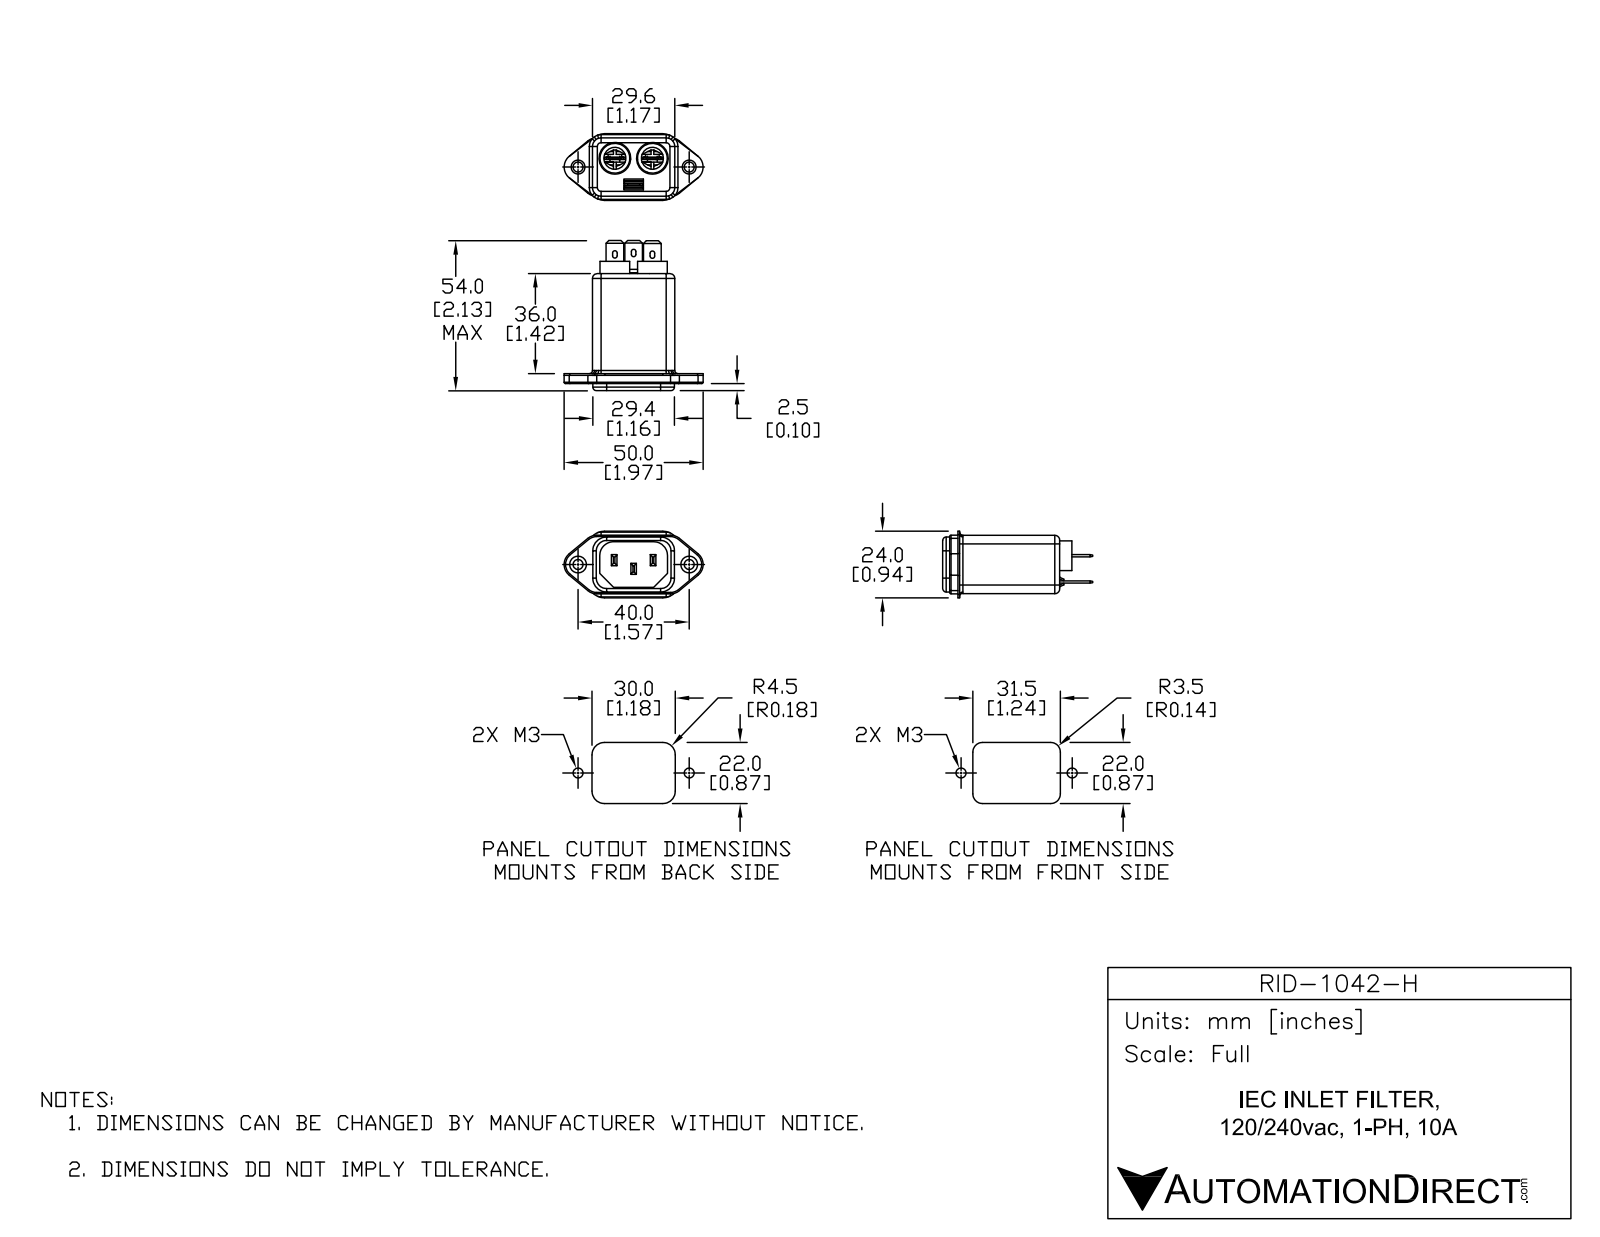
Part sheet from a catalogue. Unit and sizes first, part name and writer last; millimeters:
Units: millimetres
Overall size (bounding box): 54 × 50 × 24
Round holes (diameter × count): ⌀1.5 ×2, ⌀1.65 ×2, ⌀3.6 ×2, ⌀5 ×2, ⌀7.9 ×2, ⌀11.4 ×2, ⌀1.75 ×1
Round bosses / shafts (diameter × count): ⌀10.7 ×2
Partial cylindrical surfaces — rounded edges, fillets, slot ends (radius × count): R5 ×12, R0.3 ×11, R0.5 ×8, R1 ×8, R0.8 ×7, R1.25 ×6, R2.5 ×6, R1.75 ×4
Main face-to-face distances: 0.6, 20.4, 21, 19.8, 29, 1.05, 28.9, 36, 1.45, 11.2
Hole centre spacings: 13.5, 13.62, 26.93, 6.77, 6.78, 10.47, 10.77, 11.21
Volume: 12 008 mm³ · Surface area: 20 049 mm²
Bodies: 11 solids, 591 faces (410 planar, 142 cylindrical, 39 other)
Part name (STEP PRODUCT): ENCLOSURE A1_+; RID-1042-H; inlet body DAC-3
STEP written by: SolidWorks 2015 (AUTOMOTIVE_DESIGN)
